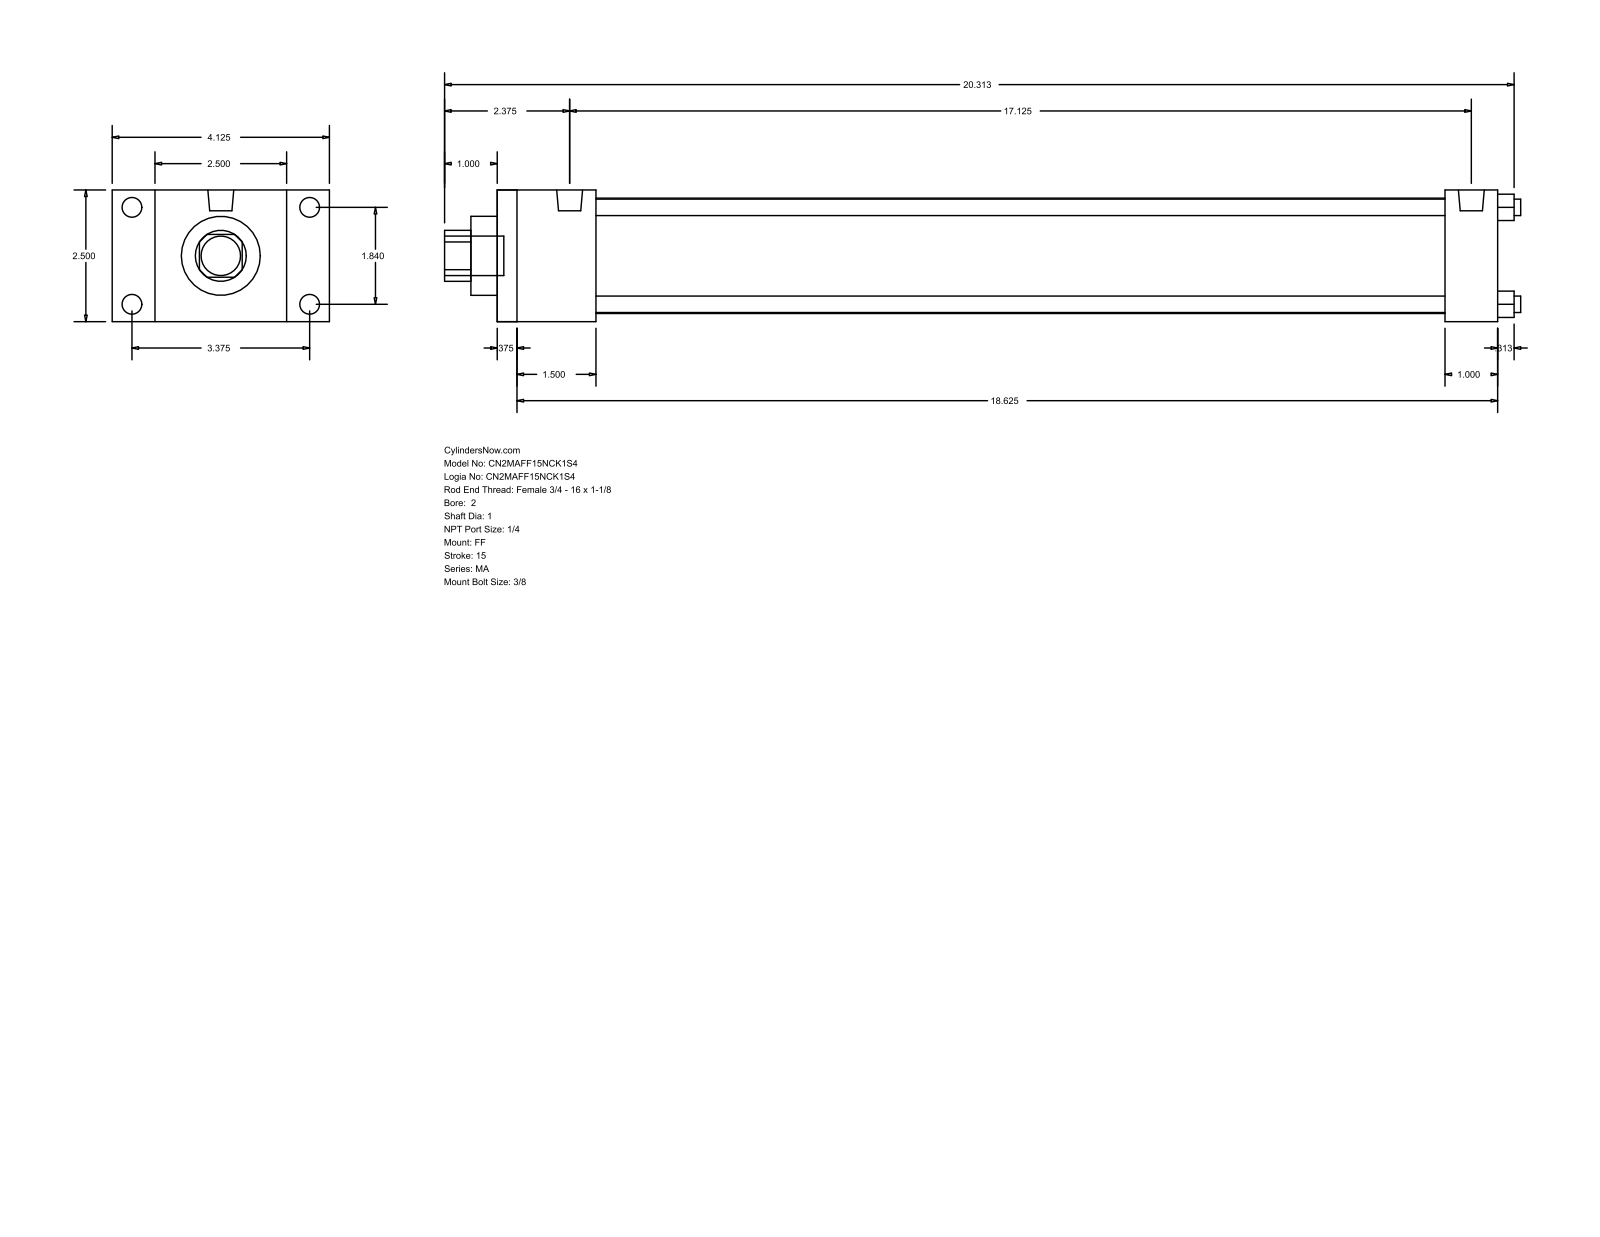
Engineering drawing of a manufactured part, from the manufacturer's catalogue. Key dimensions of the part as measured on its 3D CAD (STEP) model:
Part name (STEP PRODUCT): MA_FF__0200_1
STEP written by: GSSL Pune (CONFIG_CONTROL_DESIGN)
Units: millimetres
Bodies: 0 solids, 92 faces (64 planar, 28 cylindrical, 0 other)
Overall size (bounding box): 519.11 × 104.78 × 63.5
Round holes (diameter × count): ⌀7.94 ×4, ⌀25.4 ×1, ⌀38.1 ×1, ⌀55.63 ×1
Round bosses / shafts (diameter × count): ⌀9.53 ×4, ⌀7.94 ×4, ⌀12.49 ×2, ⌀19.05 ×1
Partial cylindrical surfaces — rounded edges, fillets, slot ends (radius × count): R12.29 ×1
Main face-to-face distances: 63.5, 482.6, 9.52, 473.08, 25.4, 20.64, 12.7, 47.63, 457.2, 38.11
Hole centre spacings: 33.05, 46.74, 66.1
